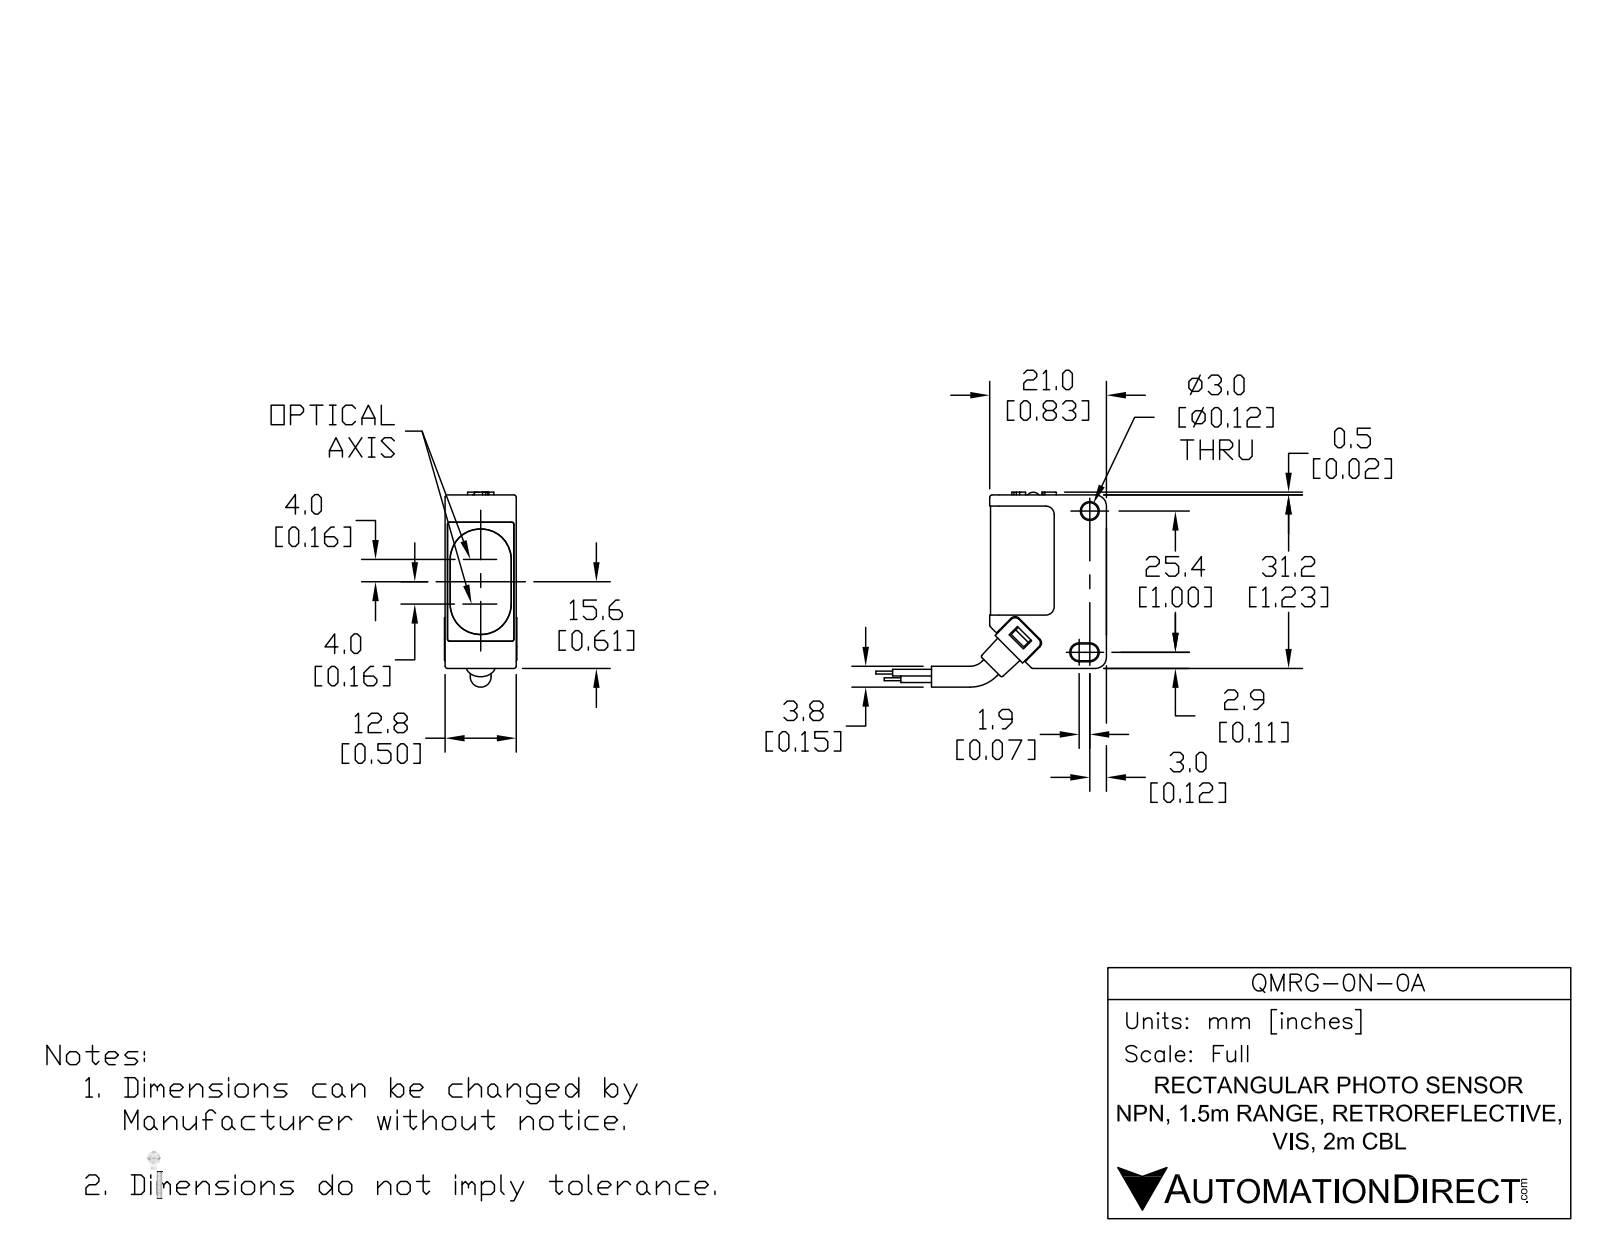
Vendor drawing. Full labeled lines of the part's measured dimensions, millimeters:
Part name (STEP PRODUCT): QMRG-0N-0A
STEP written by: SolidWorks 2017 (AUTOMOTIVE_DESIGN)
Units: millimetres
Bodies: 9 solids, 258 faces (134 planar, 100 cylindrical, 24 other)
Overall size (bounding box): 81.1 × 26.2 × 13
Volume: 7 700 mm³ · Surface area: 5 403 mm²
Round holes (diameter × count): ⌀3 ×3, ⌀3.8 ×1, ⌀5.7 ×1, ⌀7.2 ×1
Round bosses / shafts (diameter × count): ⌀3.5 ×2
Partial cylindrical surfaces — rounded edges, fillets, slot ends (radius × count): R0.4 ×13, R0.5 ×10, R1 ×8, R1.5 ×6, R0.6 ×4, R0.2 ×2, R0.9 ×2, R1.1 ×2
Main face-to-face distances: 0.5, 12.6, 1.5, 0.4, 12.8, 3.5, 12.4, 2, 12.2, 12.5
Hole centre spacings: 5.2
